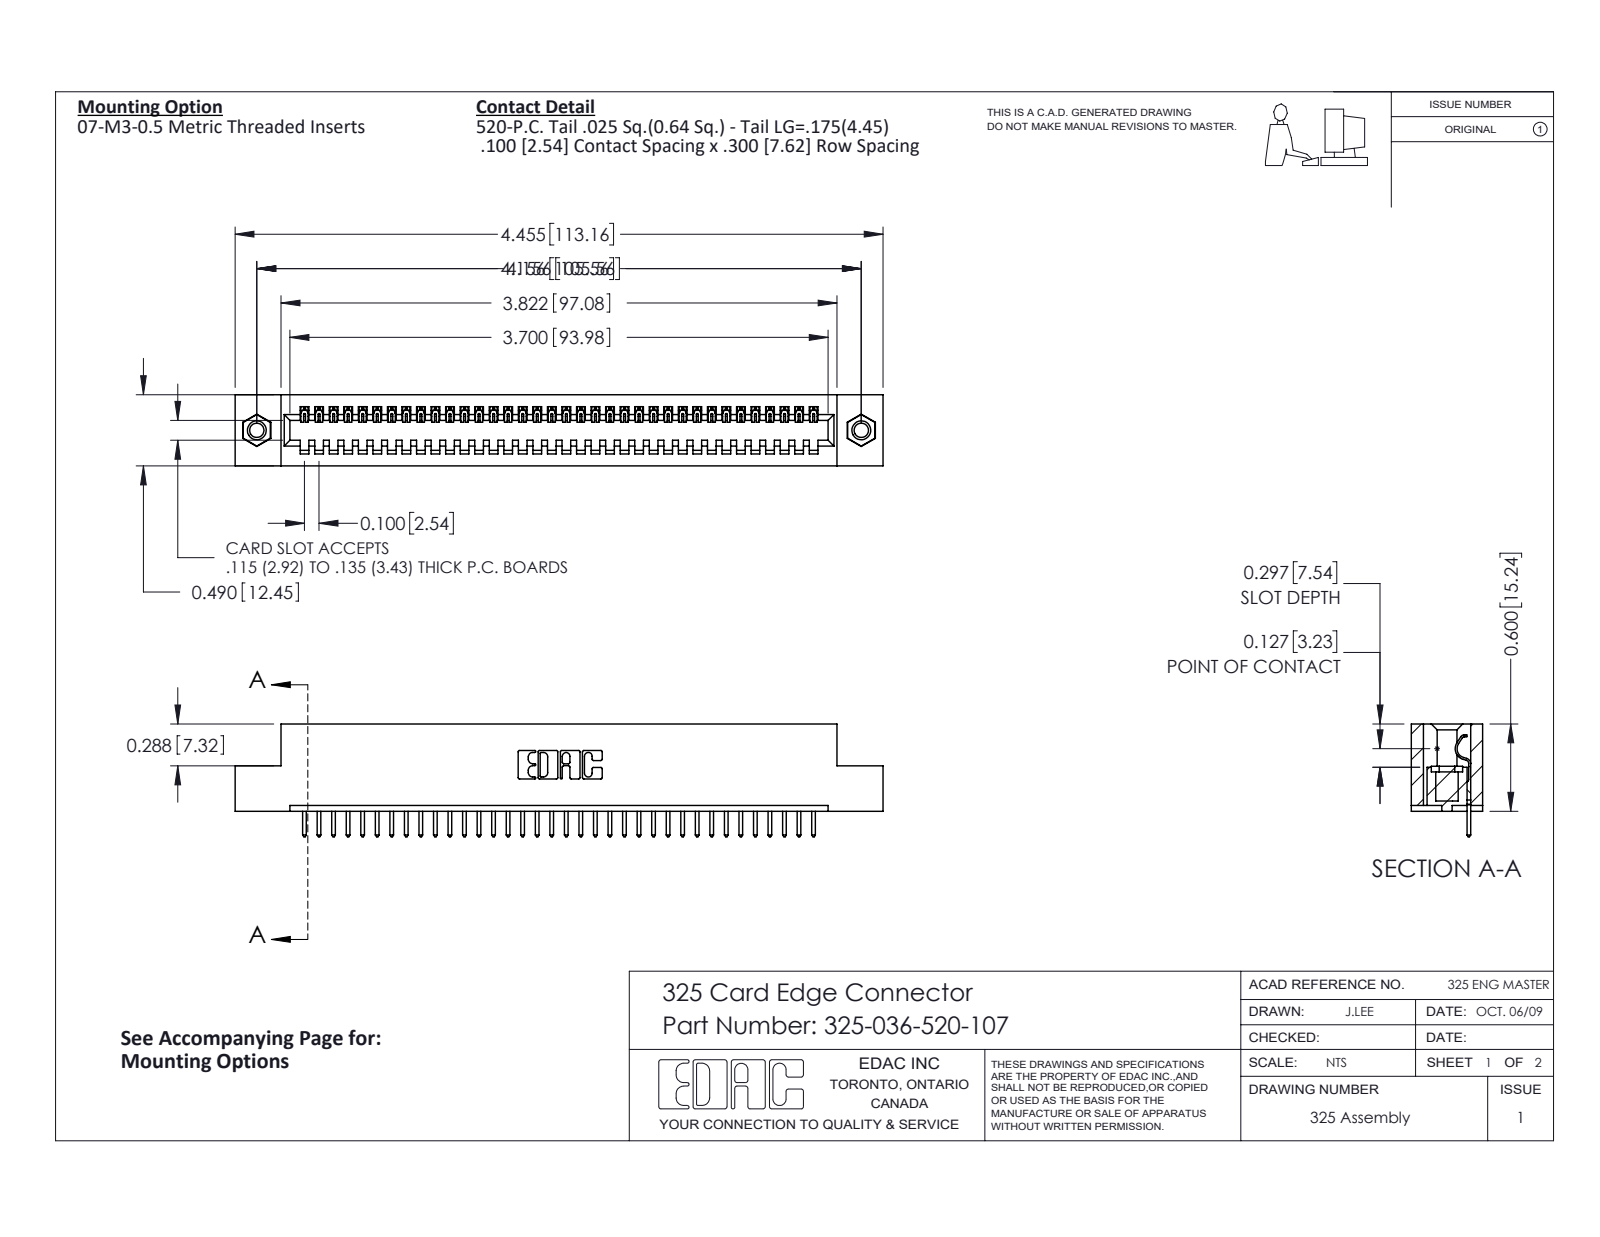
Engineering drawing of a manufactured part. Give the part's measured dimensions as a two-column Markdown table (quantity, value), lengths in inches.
| quantity | value |
| --- | --- |
| part name | 325 Part_TI; 345-250-001_345-250-005-103; 325-292-001_325-293-120; 325-036-520-107 |
| STEP written by | SolidWorks 2016 (CONFIG_CONTROL_DESIGN) |
| units | inches |
| bodies | 39 solids, 2262 faces (1614 planar, 632 cylindrical, 16 other) |
| overall size | 4.455 × 0.775 × 0.49 |
| volume | 0.867 in³ |
| surface area | 23.36 in² |
| round holes (diameter × count) | 0.098 × 2, 0.125 × 2, 0.16 × 2 |
| round bosses / shafts (diameter × count) | 0.155 × 2 |
| partial cylindrical surfaces (radius × count) | 0.006 × 72, 0.01 × 72, 0.01 × 22, 0.007 × 6, 0.031 × 6, 0.026 × 3, 0.014 × 1, 0.022 × 1 |
| main face-to-face distances | 0.083, 0.407, 0.49, 0.3, 0.107, 0.383, 0.025, 0.325, 0.56, 0.04 |
| hole center spacings | 4.156 |
